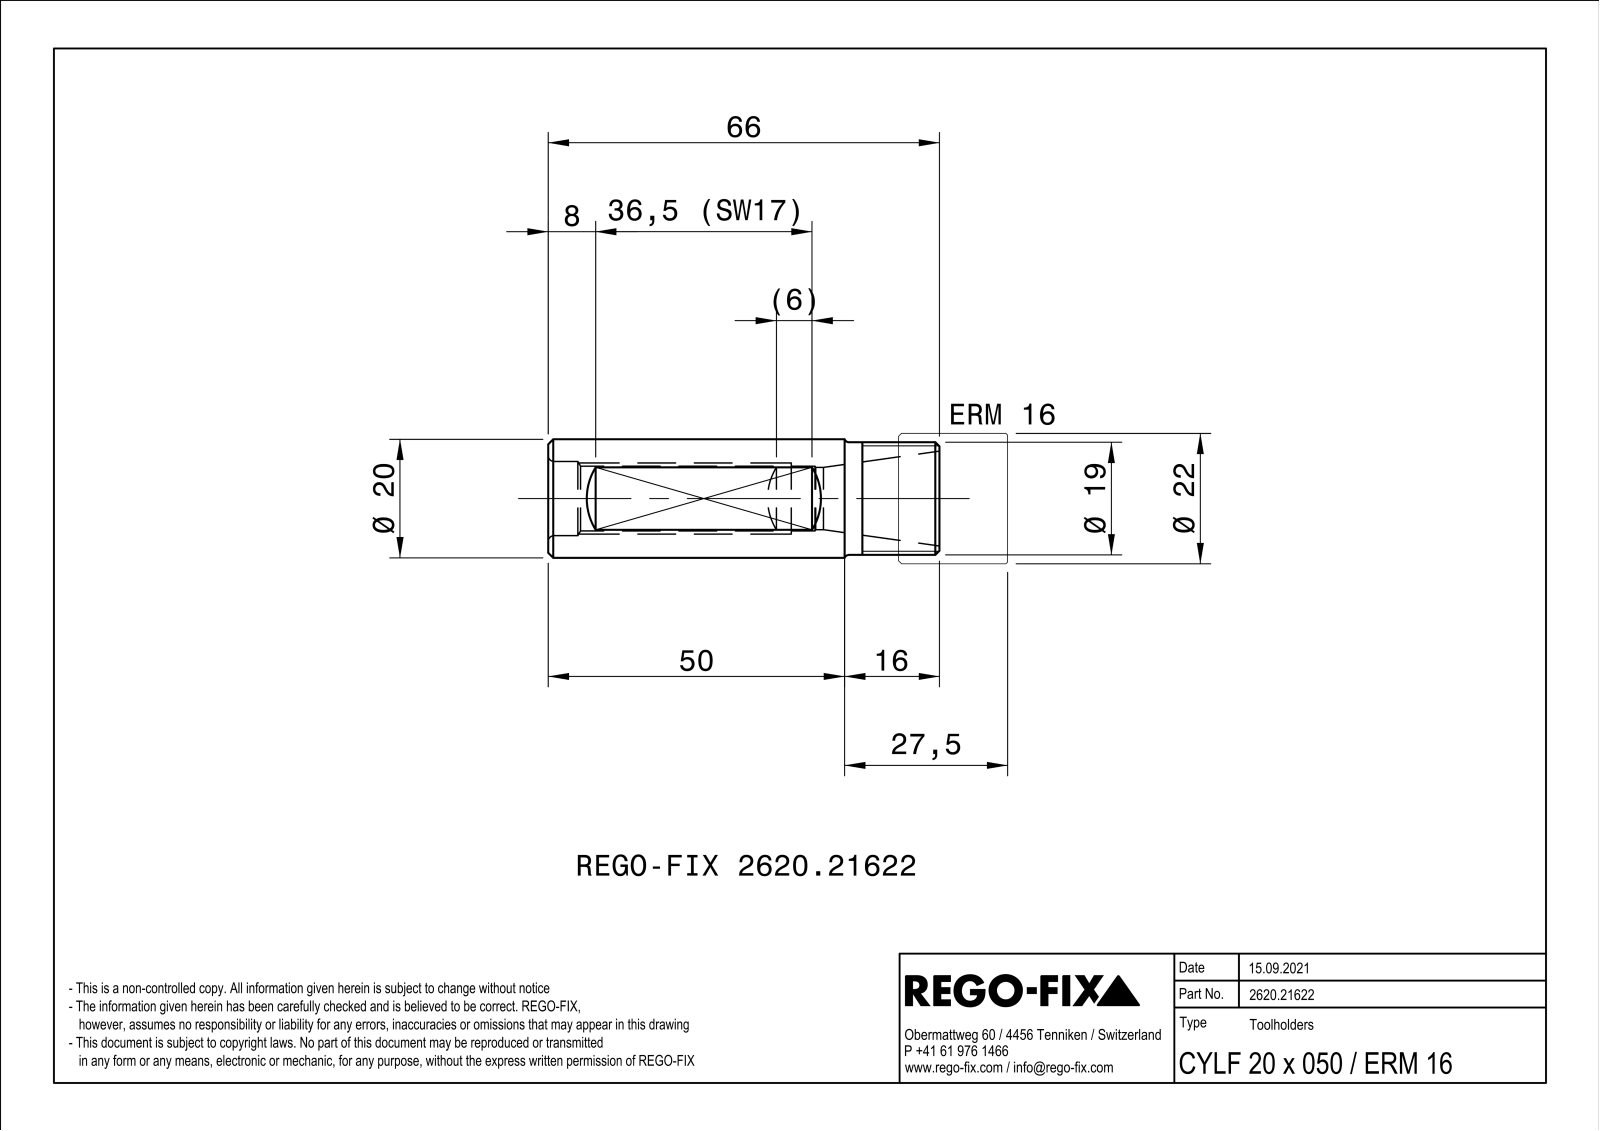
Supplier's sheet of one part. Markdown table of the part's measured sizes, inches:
| quantity | value |
| --- | --- |
| part name | NOCUT |
| STEP written by | SIEMENS PLM Software Solid Edge ST10 (AUTOMOTIVE_DESIGN) |
| units | inches |
| bodies | 1 solid, 23 faces (8 planar, 7 cylindrical, 8 other) |
| overall size | 2.598 × 0.787 × 0.787 |
| volume | 0.763 in³ |
| surface area | 10.47 in² |
| round holes (diameter × count) | 0.413 × 1, 0.43 × 1, 0.492 × 1 |
| round bosses / shafts (diameter × count) | 0.787 × 1, 0.748 × 1 |
| main face-to-face distances | 0.669, 2.598, 0.543, 0.306 |
